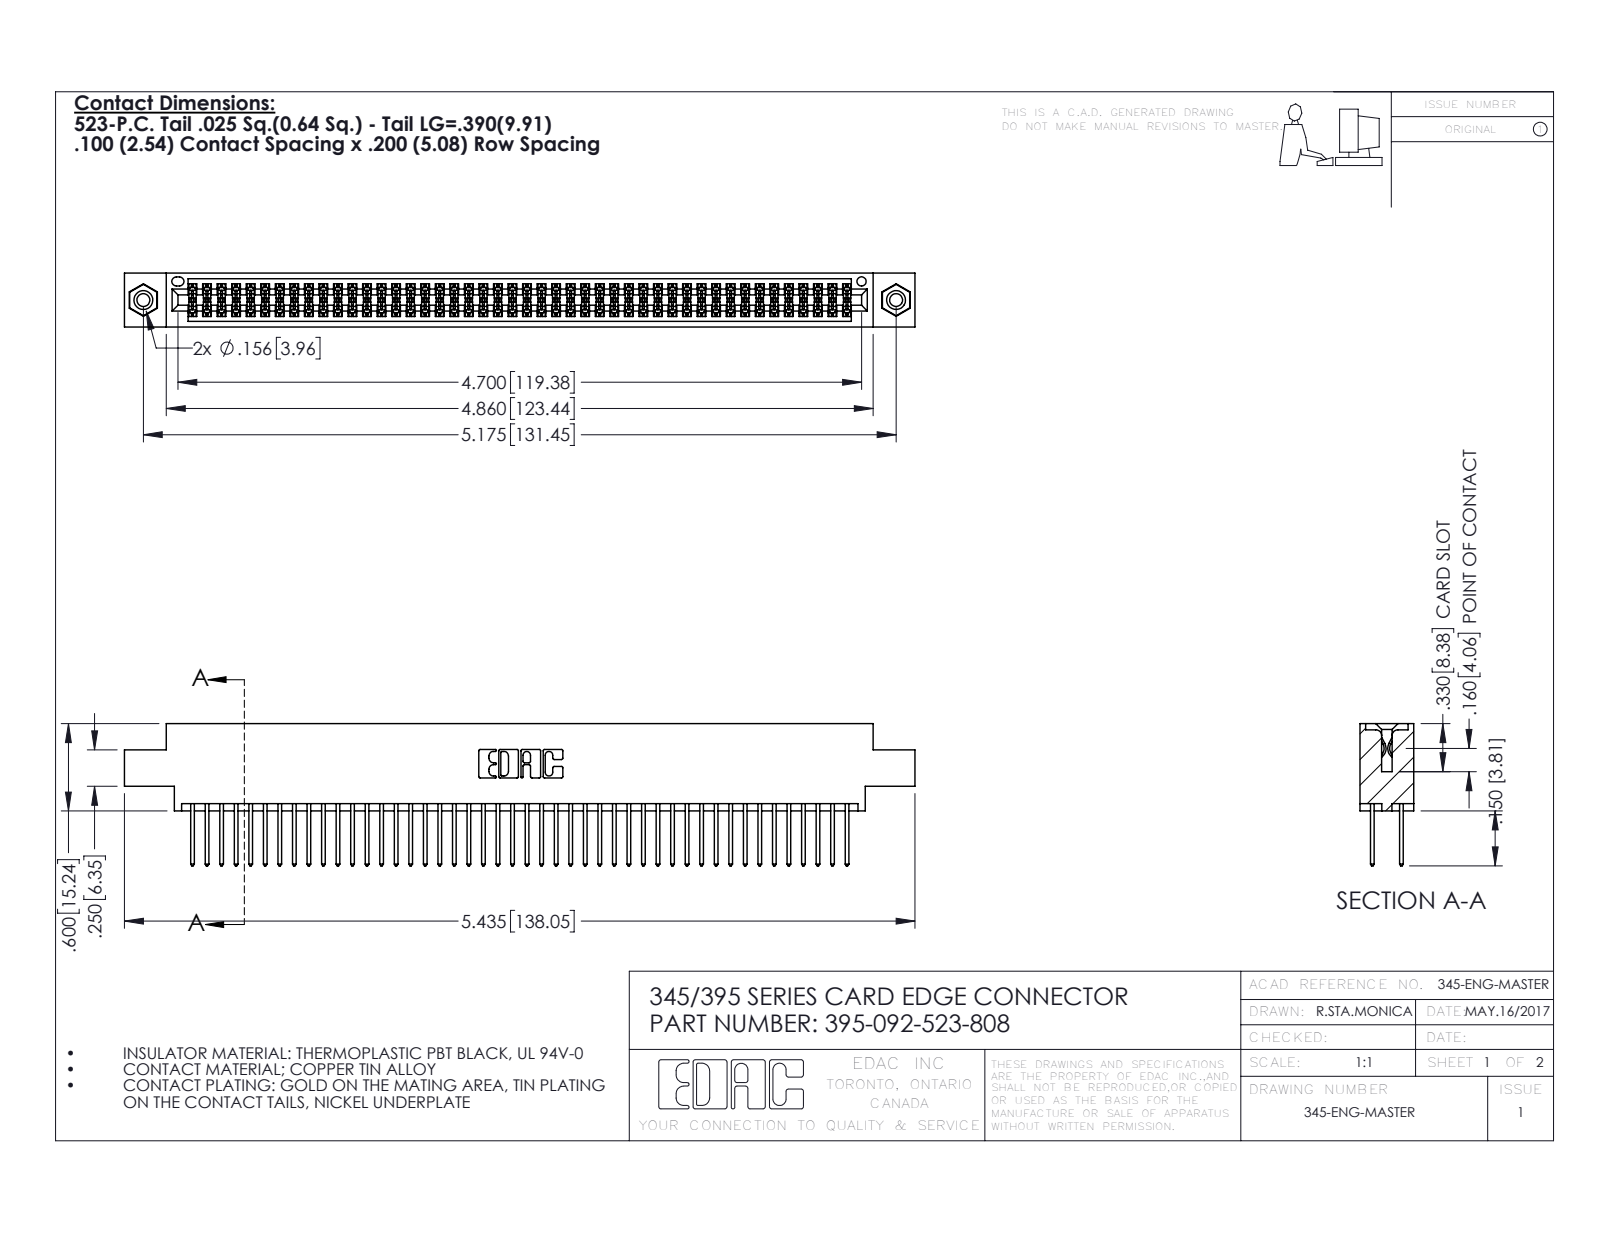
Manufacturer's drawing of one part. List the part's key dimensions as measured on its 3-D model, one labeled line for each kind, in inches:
Part name (STEP PRODUCT): 395-092-523-808; 345-292-001_345-293-123; 345-250-001_345-250-003-102; 345 Part_0.170 Offset - 0.156 Dia-TI
STEP written by: SolidWorks 2016 (CONFIG_CONTROL_DESIGN)
Units: inches
Bodies: 95 solids, 4790 faces (3152 planar, 1622 cylindrical, 16 other)
Overall size (bounding box): 5.435 × 0.977 × 0.37
Volume: 0.825 in³ · Surface area: 32.64 in²
Round holes (diameter × count): ⌀0.089 ×2, ⌀0.125 ×2, ⌀0.156 ×2, ⌀0.064 ×1
Round bosses / shafts (diameter × count): ⌀0.155 ×2
Partial cylindrical surfaces — rounded edges, fillets, slot ends (radius × count): R0.006 ×138, R0.01 ×92, R0.01 ×22, R0.007 ×6, R0.031 ×6, R0.026 ×3, R0.014 ×2, R0.019 ×2
Main face-to-face distances: 0.072, 0.298, 0.2, 0.098, 0.272, 0.025, 0.37, 0.225, 0.175, 0.149
Hole centre spacings: 0.27, 4.939, 5.175
